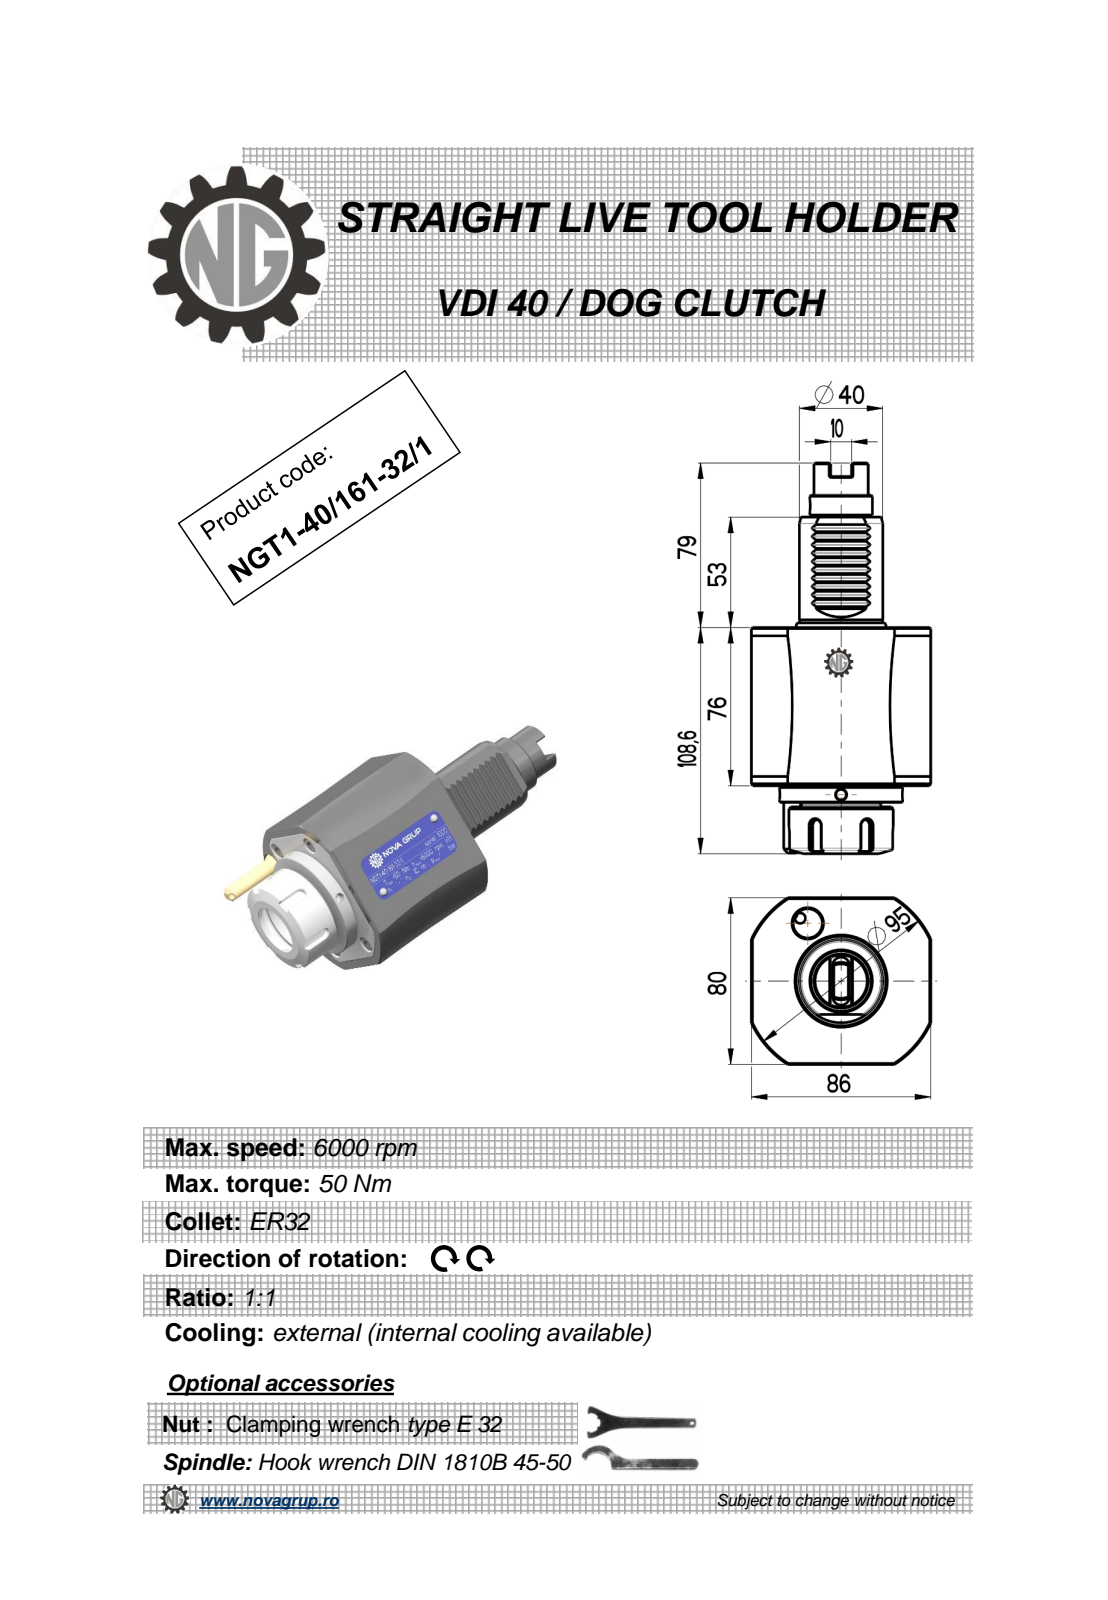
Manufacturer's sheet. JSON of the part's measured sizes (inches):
{"part_name": "NGT1_40_161_32_1", "step_written_by": "PRO/ENGINEER BY PARAMETRIC TECHNOLOGY CORPORATION, 2010280 (CONFIG_CONTROL_DESIGN)", "units": "inches", "bodies": {"solids": 1, "faces": 297, "planar": 115, "cylindrical": 79, "other": 103}, "overall_size": [7.386, 3.386, 3.15], "volume_in3": 37.54, "surface_area_in2": 85.08, "round_holes": [[0.197, 3], [0.118, 1], [0.165, 1], [1.063, 1]], "round_bosses_or_shafts": [[2.323, 1], [1.969, 1], [1.89, 1], [1.614, 1], [1.575, 1], [1.181, 1], [1.024, 1], [0.315, 1]], "partial_cylinders_radius": [[0.012, 10], [0.009, 6], [0.01, 6], [0.118, 5], [0.02, 2], [0.492, 1], [1.87, 1]], "face_to_face_distances": [2.992, 3.15, 3.386, 3.307, 0.315, 0.02, 0.111, 3.012, 0.295, 4.098], "hole_center_spacings": [1.575, 5.463]}
